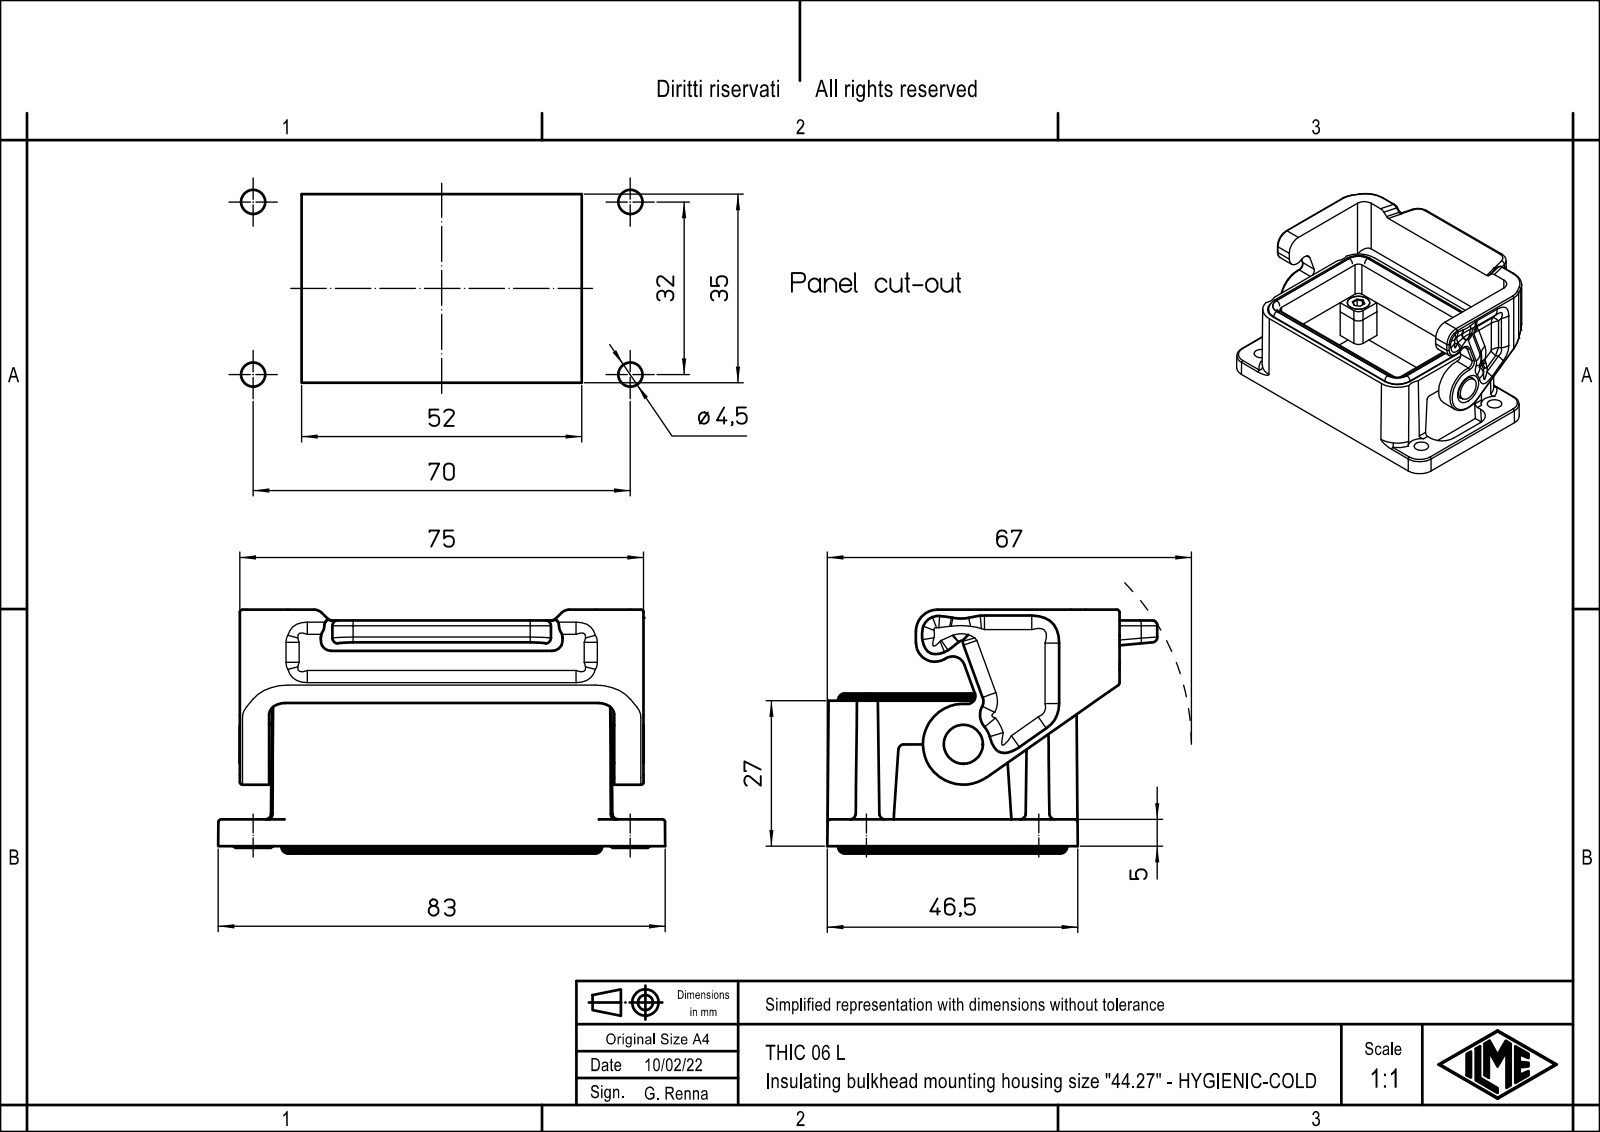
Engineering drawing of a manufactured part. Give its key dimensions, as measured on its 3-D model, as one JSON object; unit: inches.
{"part_name": "53620_D; THIH_06_L", "step_written_by": "Creo Elements/Direct Modeling 20.1B 02-Apr-2019 (C) Parametric Technology GmbH (AUTOMOTIVE_DESIGN)", "units": "inches", "bodies": {"solids": 1, "faces": 627, "planar": 254, "cylindrical": 193, "other": 180}, "overall_size": [3.268, 2.411, 1.781], "volume_in3": 2.928, "surface_area_in2": 47.16, "round_holes": [[0.098, 4], [0.177, 4], [0.272, 4]], "round_bosses_or_shafts": [[0.189, 4], [0.276, 1]], "partial_cylinders_radius": [[0.051, 32], [0.039, 24], [0.106, 12], [0.217, 12], [0.059, 11], [0.079, 11], [0.197, 10], [0.118, 7]], "face_to_face_distances": [0.22, 2.265, 0.079, 0.217, 2.736, 0.197, 2.52, 0.316, 0.866, 1.063], "hole_center_spacings": [0.521, 1.269, 2.246, 2.527, 1.063, 1.26, 1.732, 2.032]}
